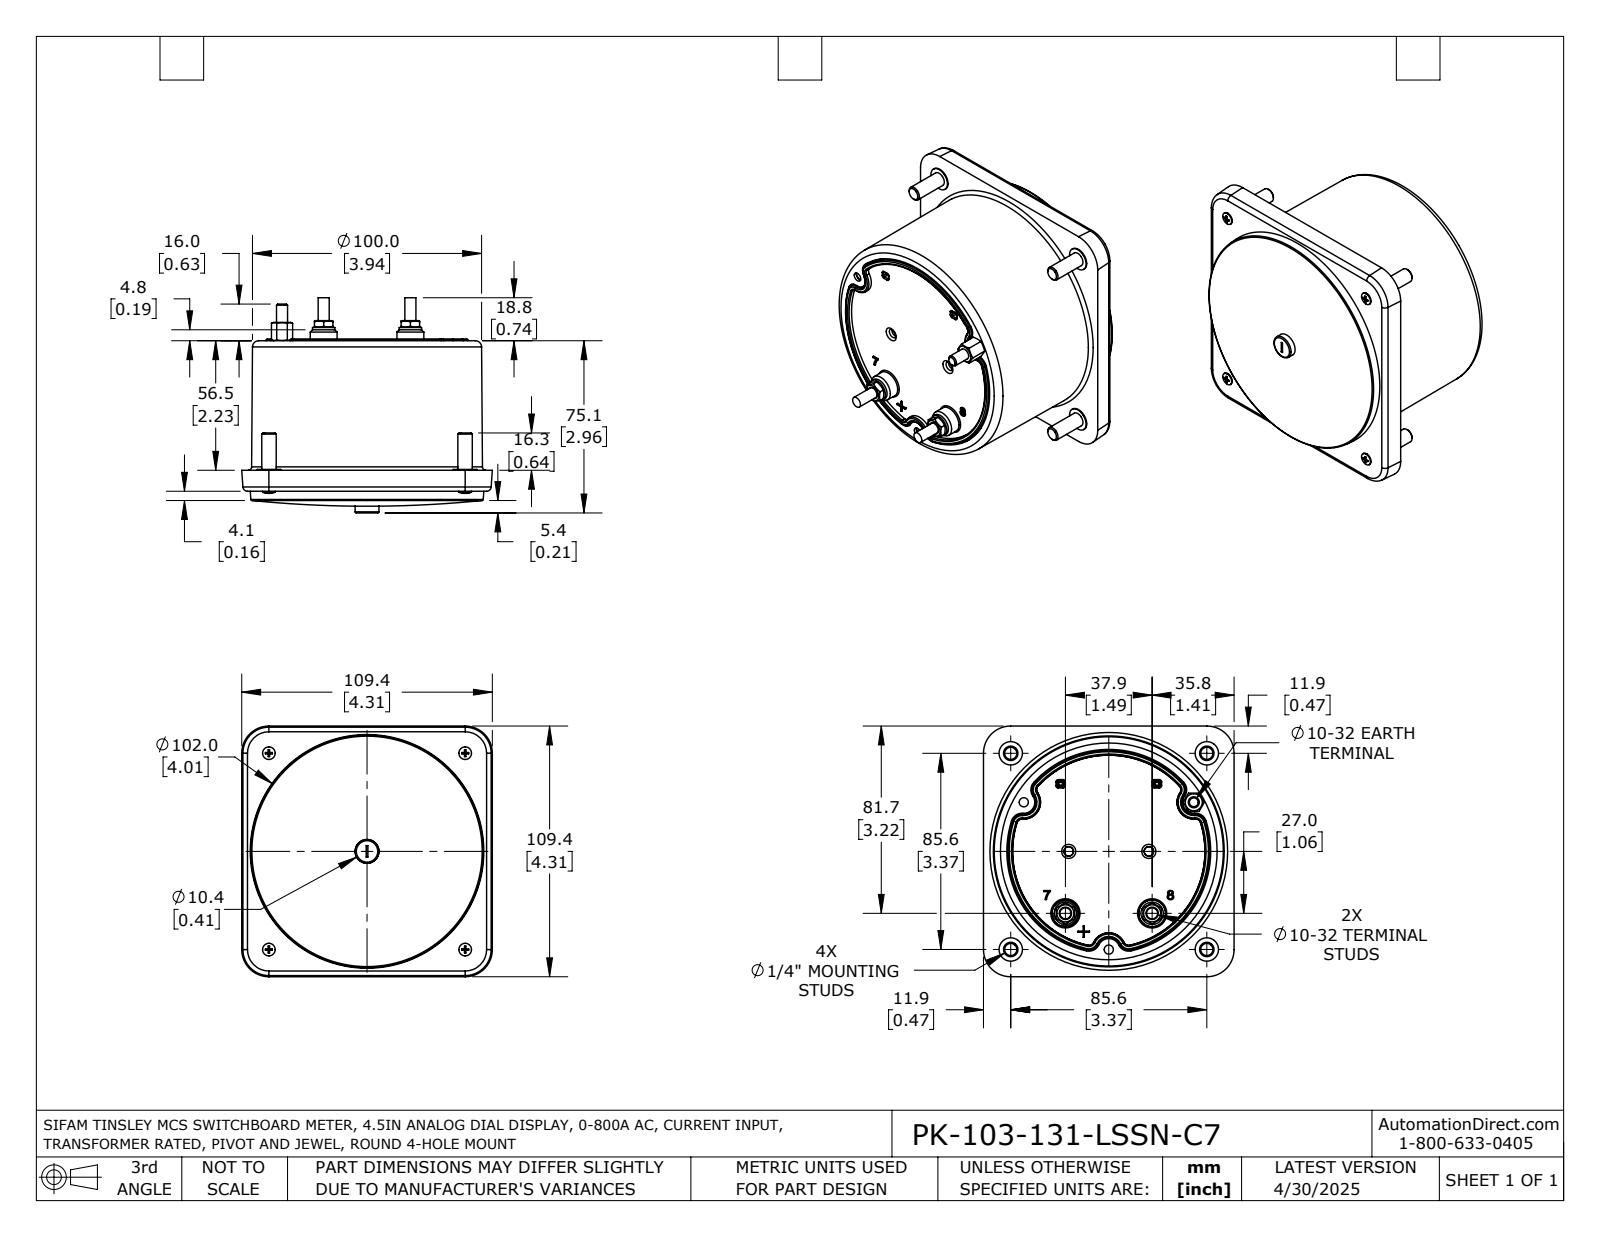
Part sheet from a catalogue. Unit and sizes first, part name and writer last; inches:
Units: inches
Overall size (bounding box): 4.307 × 4.307 × 3.697
Round holes (diameter × count): ⌀0.094 ×4, ⌀0.138 ×4, ⌀0.315 ×4, ⌀0.157 ×3, ⌀0.209 ×2
Round bosses / shafts (diameter × count): ⌀0.402 ×4, ⌀0.248 ×4, ⌀0.217 ×4, ⌀0.114 ×4, ⌀0.19 ×3, ⌀0.384 ×2, ⌀0.146 ×1
Partial cylindrical surfaces — rounded edges, fillets, slot ends (radius × count): R0.02 ×24, R0.189 ×9, R0.079 ×4, R1.752 ×1
Main face-to-face distances: 2.177, 2.537, 0.36, 0.048, 2.225, 2.585, 0.489, 2.715, 2.667, 0.129
Hole centre spacings: 3.372, 3.37, 3.374, 3.378, 3.38, 4.769, 0.971, 1.126
Volume: 36.28 in³ · Surface area: 82.21 in²
Bodies: 1 solid, 609 faces (167 planar, 141 cylindrical, 301 other)
Part name (STEP PRODUCT): PK-103-131-LSSN-C7
STEP written by: SolidWorks 2021 (AUTOMOTIVE_DESIGN)
